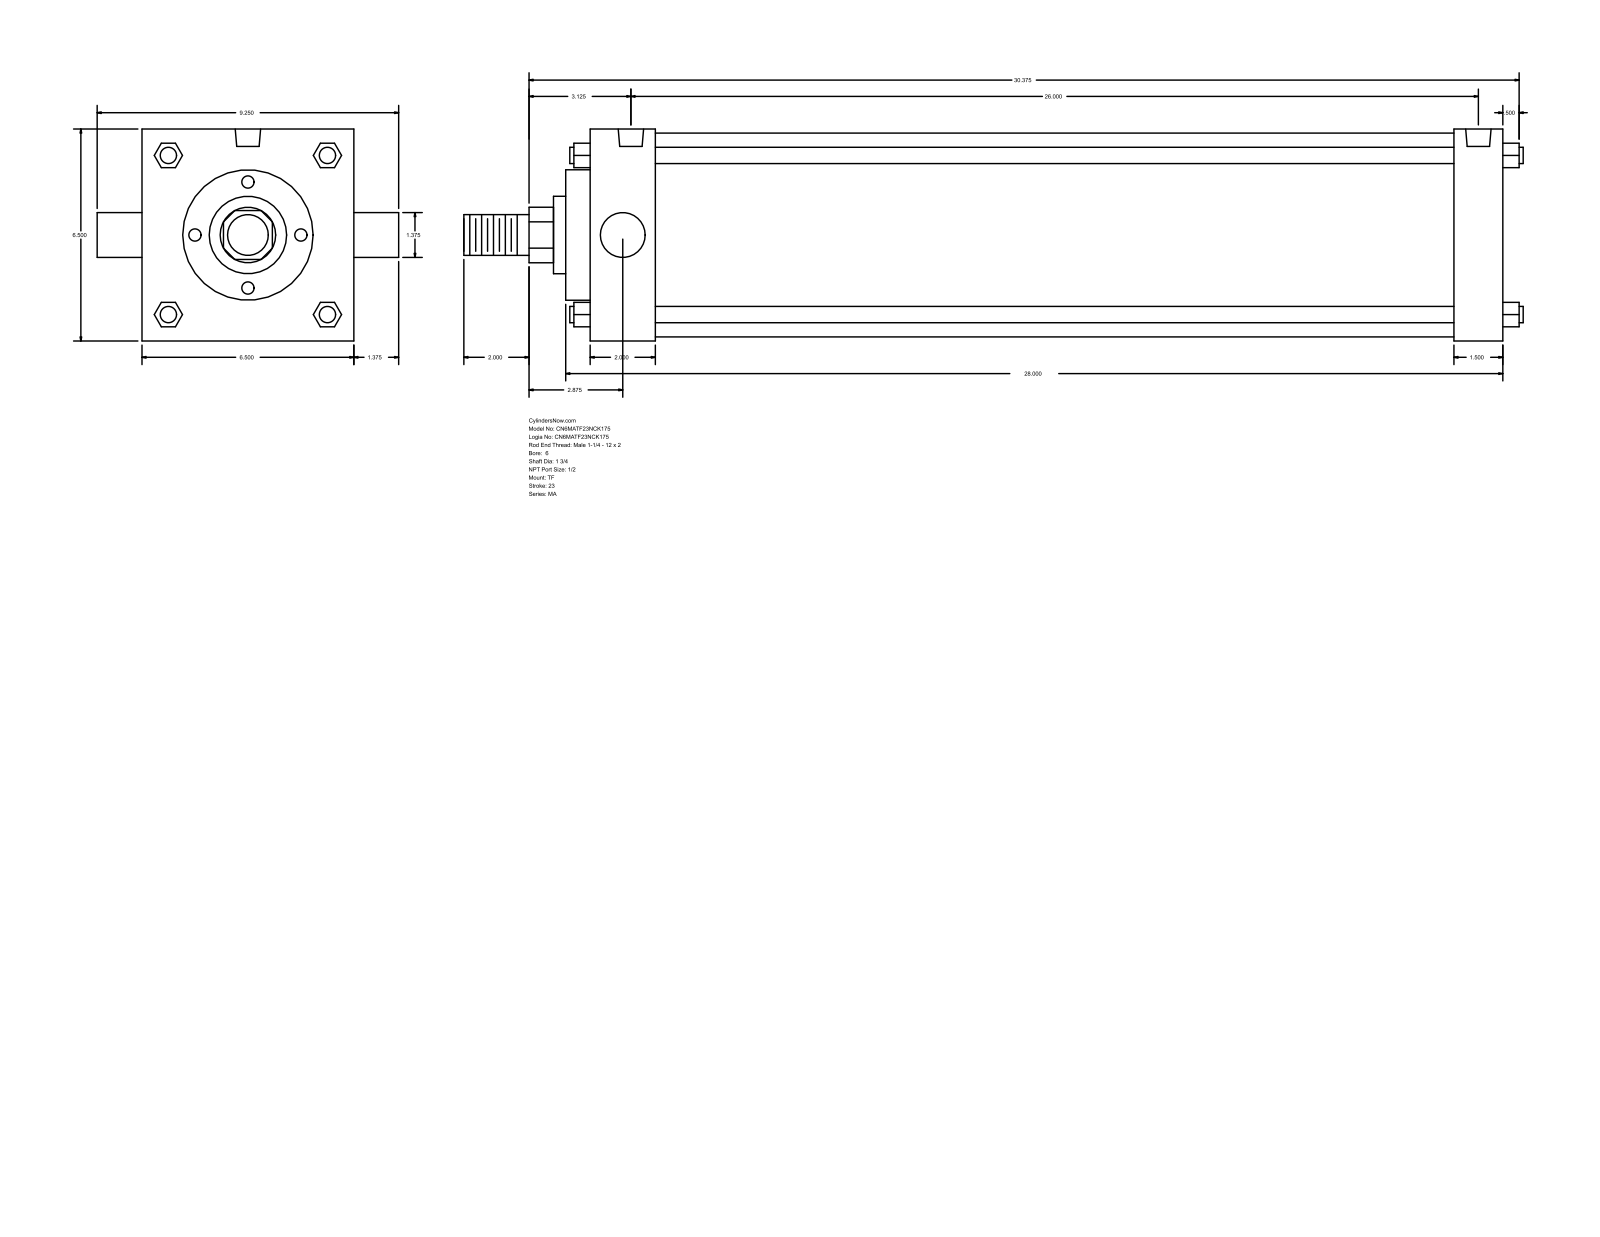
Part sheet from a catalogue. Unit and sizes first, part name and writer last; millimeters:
Units: millimetres
Overall size (bounding box): 825.5 × 234.95 × 165.1
Round holes (diameter × count): ⌀17.46 ×3, ⌀19.77 ×2
Round bosses / shafts (diameter × count): ⌀12.7 ×4, ⌀158.75 ×1, ⌀101.6 ×1, ⌀60.33 ×1, ⌀44.45 ×1, ⌀34.92 ×1, ⌀31.75 ×1
Partial cylindrical surfaces — rounded edges, fillets, slot ends (radius × count): R21.63 ×1
Main face-to-face distances: 165.1, 711.21, 19.05, 38.1, 50.8, 660.41, 673.11, 622.31, 69.85, 692.16
Hole centre spacings: 660.39
Bodies: 0 solids, 122 faces (93 planar, 29 cylindrical, 0 other)
Part name (STEP PRODUCT): MA_TF__0600_1.75
STEP written by: GSSL Pune (CONFIG_CONTROL_DESIGN)
